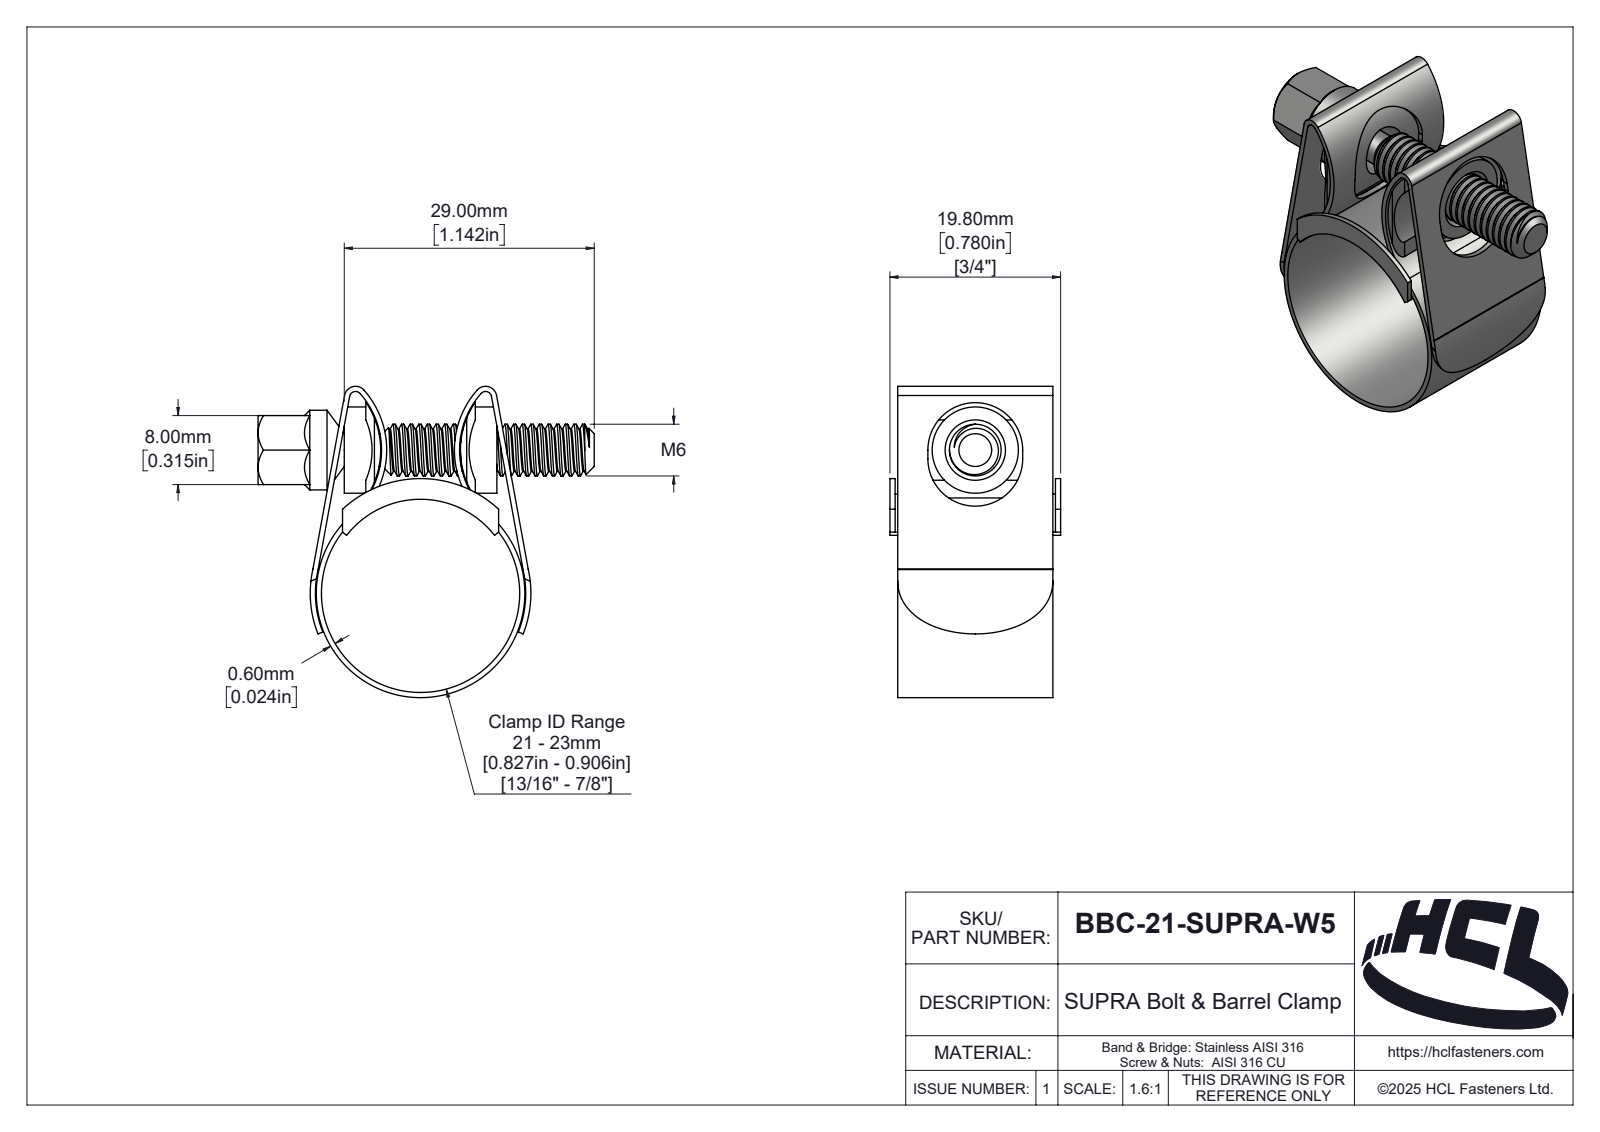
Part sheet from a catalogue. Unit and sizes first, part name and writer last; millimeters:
Units: millimetres
Overall size (bounding box): 39 × 36.1 × 19.8
Round holes (diameter × count): ⌀23 ×1
Round bosses / shafts (diameter × count): ⌀10 ×1, ⌀9.24 ×1, ⌀6 ×1, ⌀3.8 ×1
Partial cylindrical surfaces — rounded edges, fillets, slot ends (radius × count): R1 ×4, R0.7 ×2, R1.3 ×2, R2 ×2, R2.6 ×2, R5.5 ×2, R8.79 ×2, R9.79 ×2
Main face-to-face distances: 0.6, 0.9, 18.9, 18, 2.5, 15.2, 8, 19.2, 18.3, 17.7
Volume: 3 327 mm³ · Surface area: 7 840 mm²
Bodies: 5 solids, 283 faces (44 planar, 159 cylindrical, 80 other)
Part name (STEP PRODUCT): BBC-21-SUPRA-W5
STEP written by: SolidWorks 2025 (AUTOMOTIVE_DESIGN)
